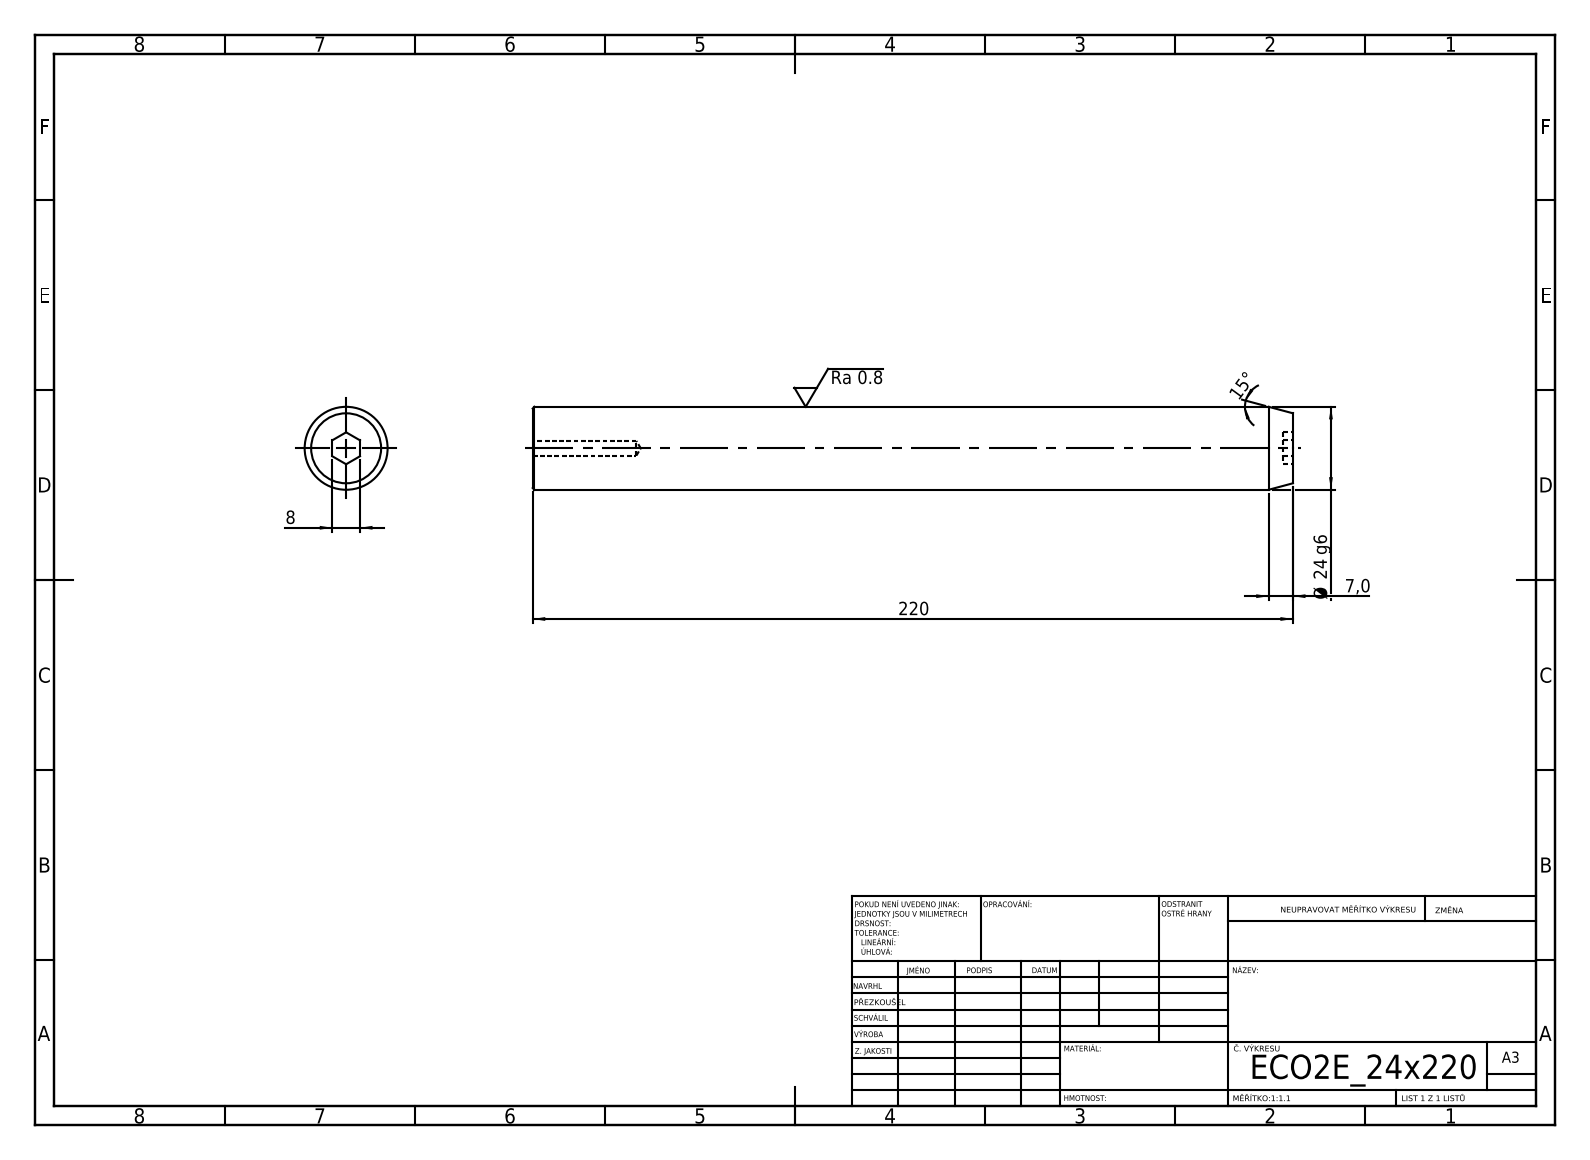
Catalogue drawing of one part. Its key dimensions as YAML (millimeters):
step_written_by: "SolidWorks 2019 (CONFIG_CONTROL_DESIGN)"
units: millimeters
bodies: {solids: 1, faces: 19, planar: 9, cylindrical: 4, other: 6}
overall_size: [220, 24, 24]
volume: 98471
surface_area: 17791
round_holes:
  - {diameter: 4.2, count: 1}
round_bosses_or_shafts:
  - {diameter: 24, count: 1}
face_to_face_distances: [220, 2.8, 217.2, 8]
